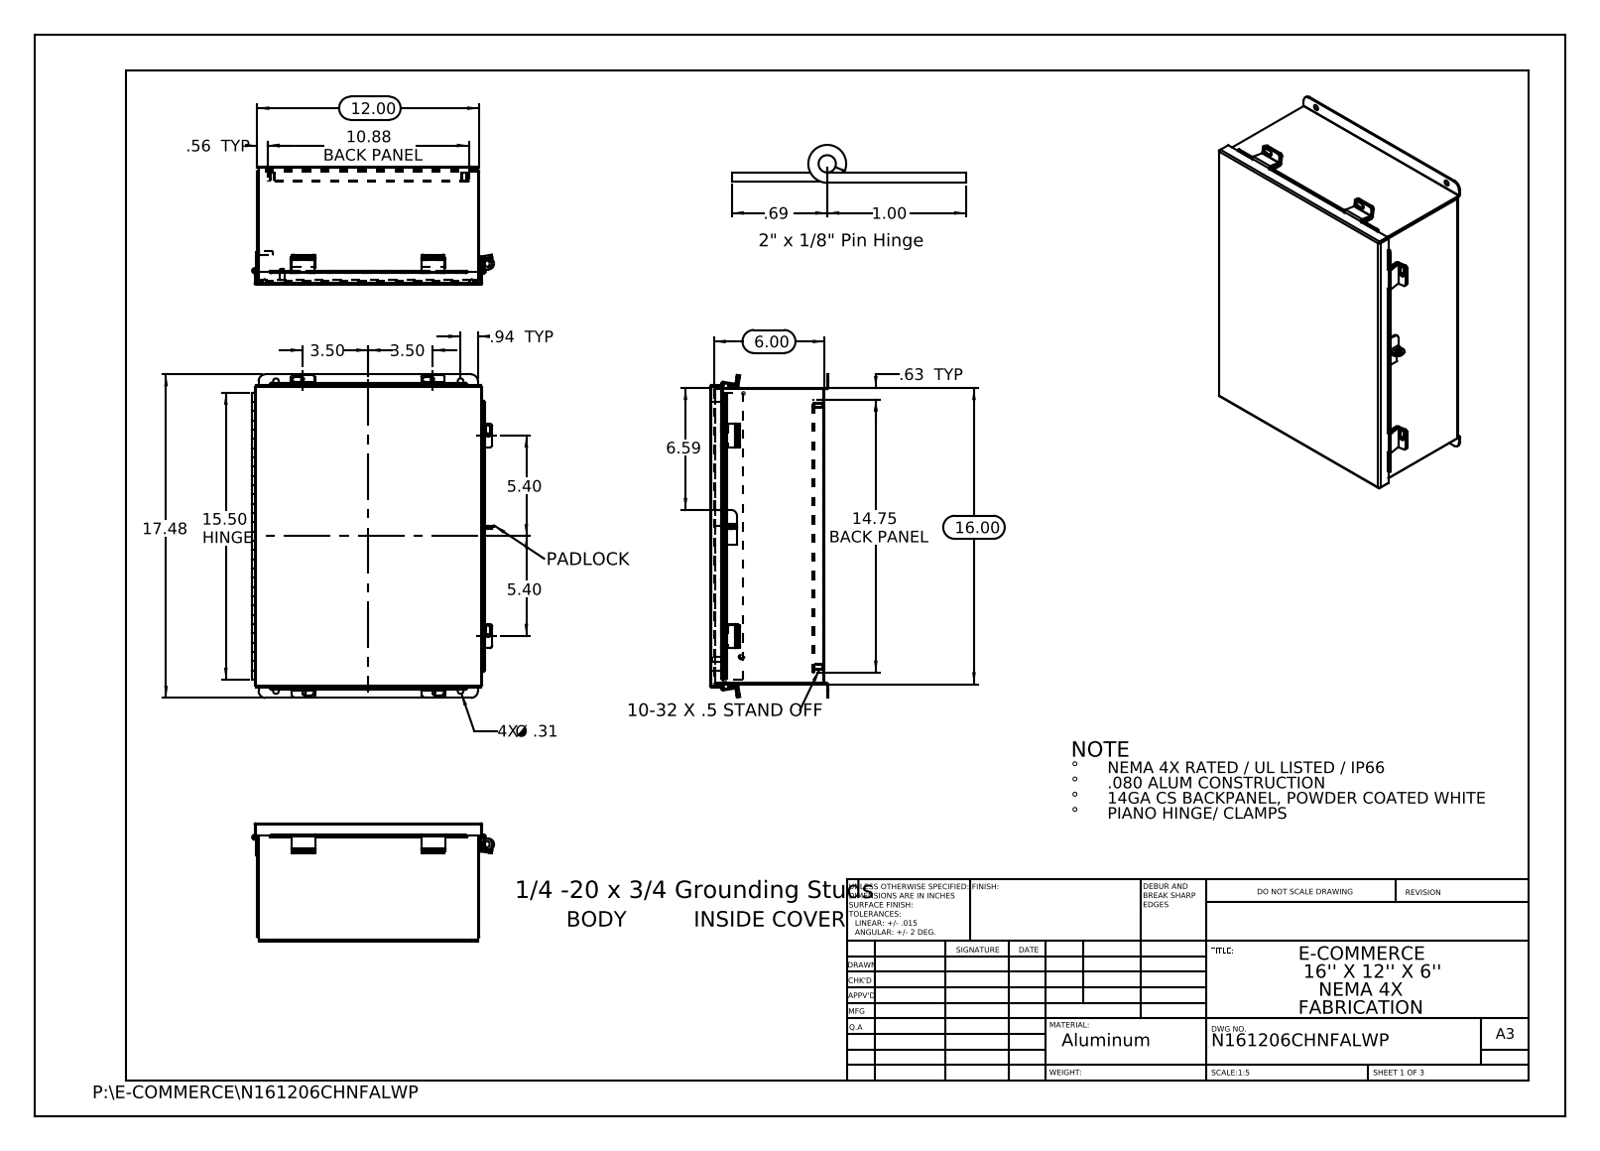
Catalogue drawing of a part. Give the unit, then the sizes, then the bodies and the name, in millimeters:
Units: millimetres
Overall size (bounding box): 443.9 × 332 × 162.3
Round holes (diameter × count): ⌀6.4 ×10, ⌀4.7 ×4, ⌀7.9 ×4, ⌀3.2 ×1, ⌀3.2 ×1, ⌀9.5 ×1, ⌀9.5 ×1
Round bosses / shafts (diameter × count): ⌀8 ×4, ⌀8 ×2, ⌀6 ×2, ⌀6.9 ×1, ⌀6.4 ×1
Partial cylindrical surfaces — rounded edges, fillets, slot ends (radius × count): R3.2 ×22, R0.3 ×13, R0.2 ×12, R2.2 ×12, R3.4 ×12, R2.1 ×6, R2.5 ×6, R9.5 ×4
Main face-to-face distances: 1.9, 155.7, 153.7, 157.6, 302.9, 1.9, 143, 14.6, 12.7, 141
Hole centre spacings: 33.4, 260.6, 391.8, 469.4, 177.8, 253.4, 263.5, 358.8
Volume: 1 236 000 mm³ · Surface area: 1 325 000 mm²
Bodies: 27 solids, 866 faces (539 planar, 307 cylindrical, 20 other)
Part name (STEP PRODUCT): HW-CLH-JH-20154; N161206CHNFALWP Hinge Cover Side JIC; N161206CHNFALWP JIC Bottom; N161206CHNFALWP _JIC Hinge (+8 more)
STEP written by: SolidWorks 2013 (CONFIG_CONTROL_DESIGN)
